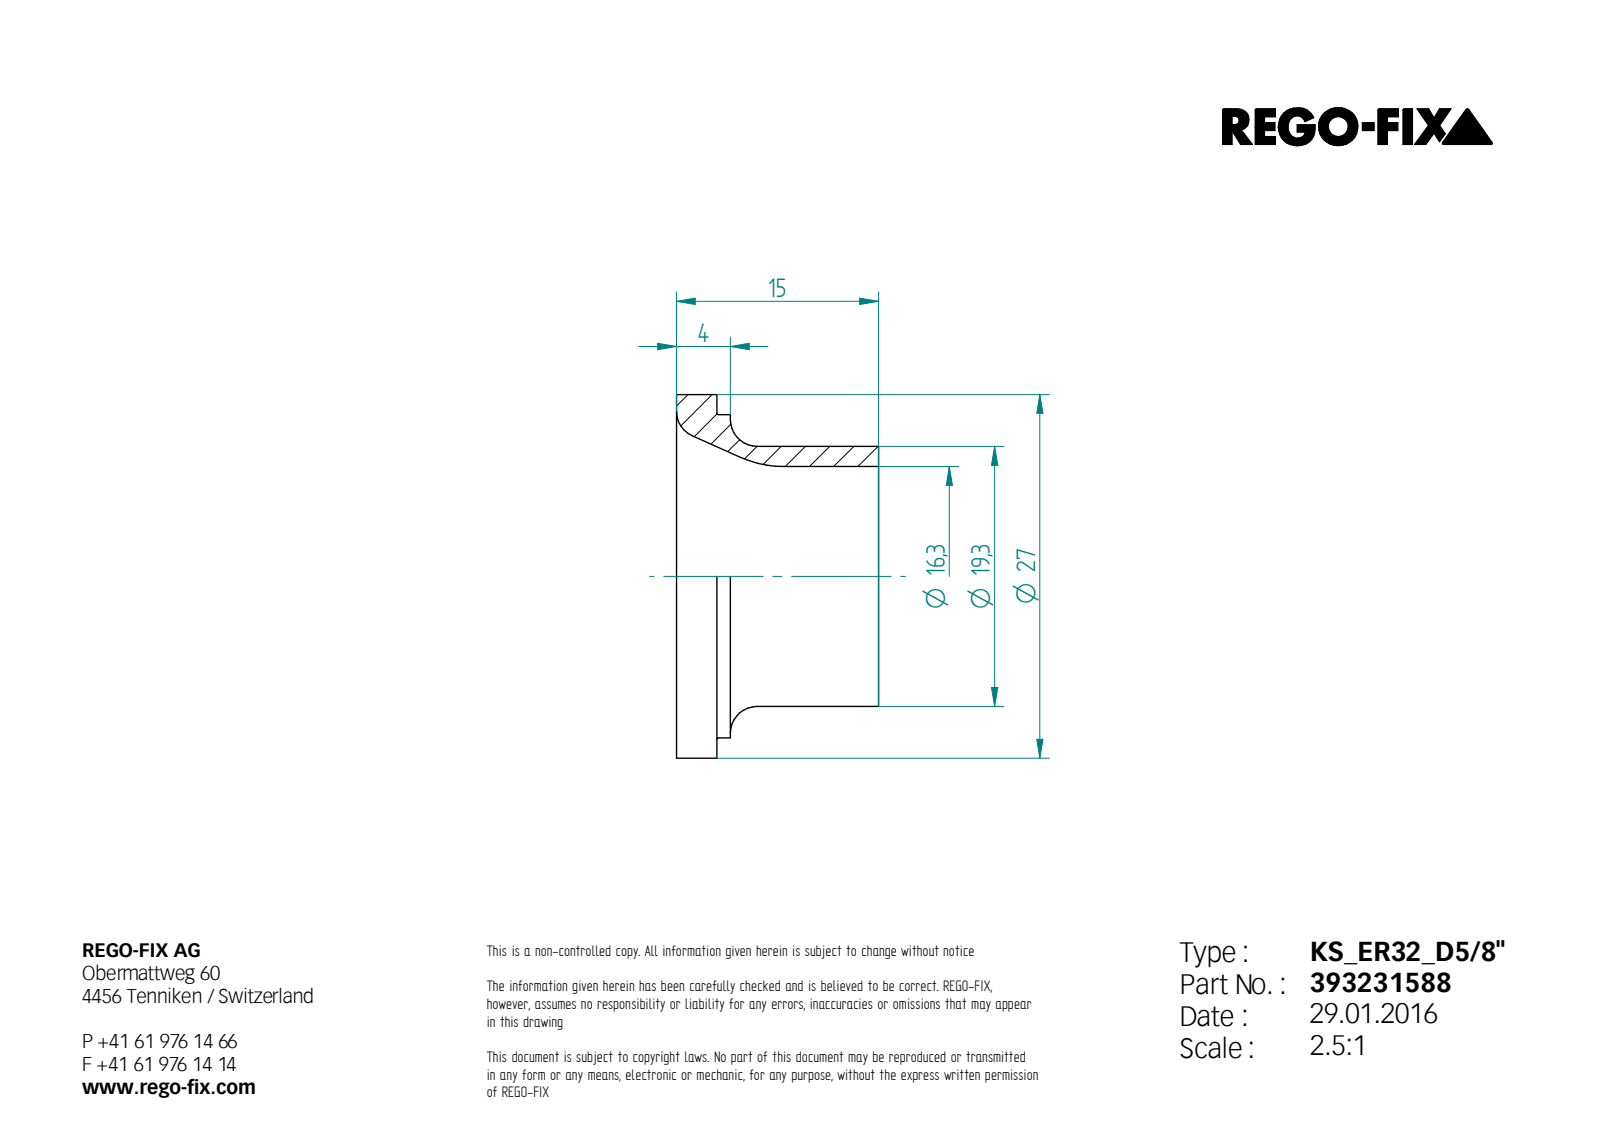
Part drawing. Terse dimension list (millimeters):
written by: Unknown (AUTOMOTIVE_DESIGN)
unit: mm
bodies: 1 solid, 13 faces (4 planar, 4 cylindrical, 5 other)
size: 27 × 27 × 15
volume: 1 778 mm³; area: 2 341 mm²
holes: 1× ⌀16.3
bosses: 1× ⌀27, 1× ⌀24, 1× ⌀19.3
face distances: 3, 15, 12, 4, 1, 11
